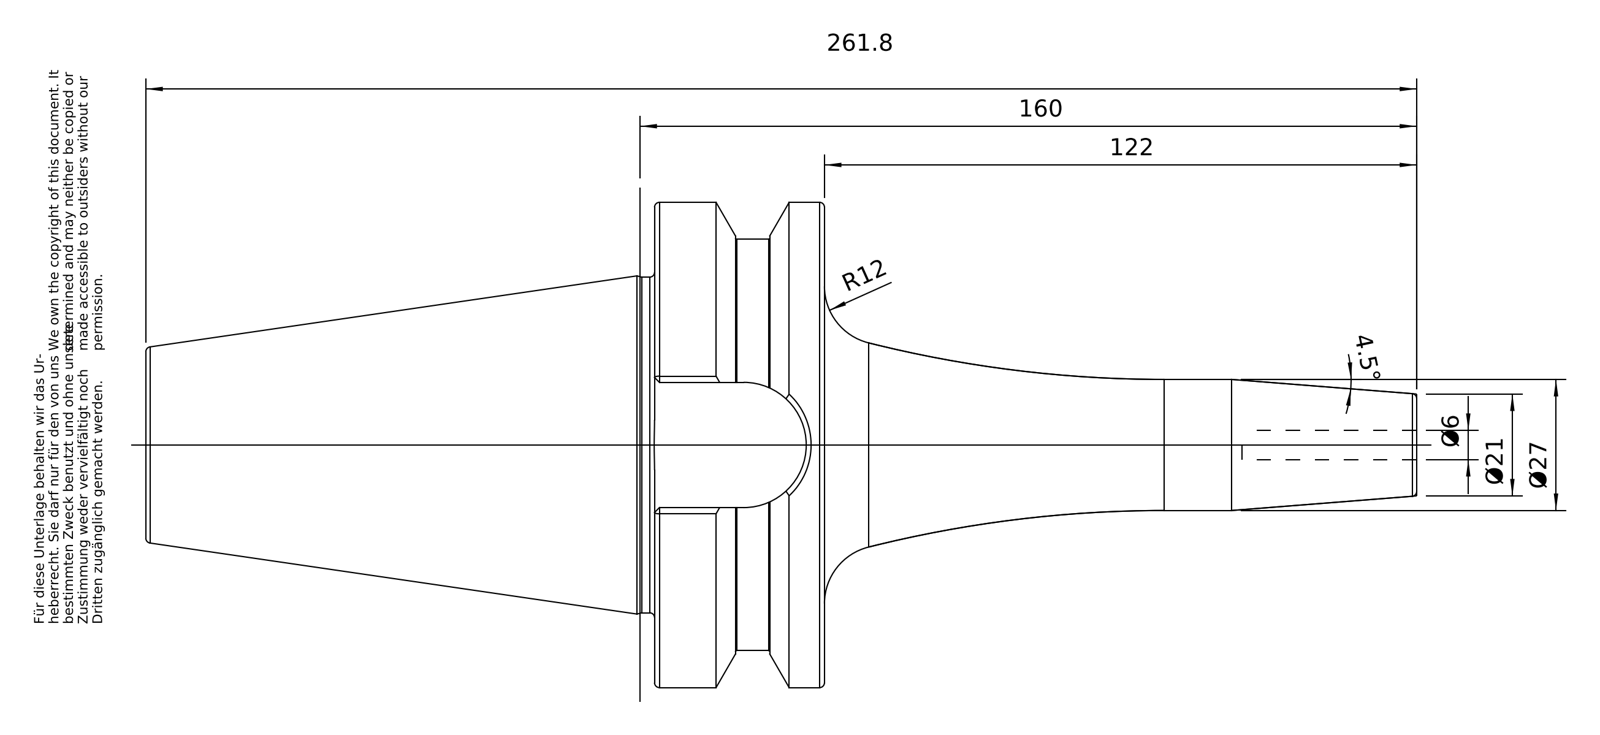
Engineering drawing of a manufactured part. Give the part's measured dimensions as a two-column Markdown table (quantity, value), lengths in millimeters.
| quantity | value |
| --- | --- |
| part name | 50-642-06 |
| STEP written by | PRO/ENGINEER BY PARAMETRIC TECHNOLOGY CORPORATION, 2010430 (CONFIG_CONTROL_DESIGN) |
| units | millimeters |
| bodies | 1 solid, 98 faces (26 planar, 22 cylindrical, 50 other) |
| overall size | 261.8 × 99.97 × 99.97 |
| volume | 558 919 mm³ |
| surface area | 62 328 mm² |
| round holes (diameter × count) | 6 × 1, 20.75 × 1, 25.02 × 1, 25.7 × 1 |
| round bosses / shafts (diameter × count) | 99.97 × 1, 84.75 × 1, 69.15 × 1, 27 × 1, 24.01 × 1 |
| partial cylindrical surfaces (radius × count) | 12.9 × 1 |
| main face-to-face distances | 35, 70.4, 104.8, 139.8, 25.8, 261.8, 157, 122, 48, 56.8 |
